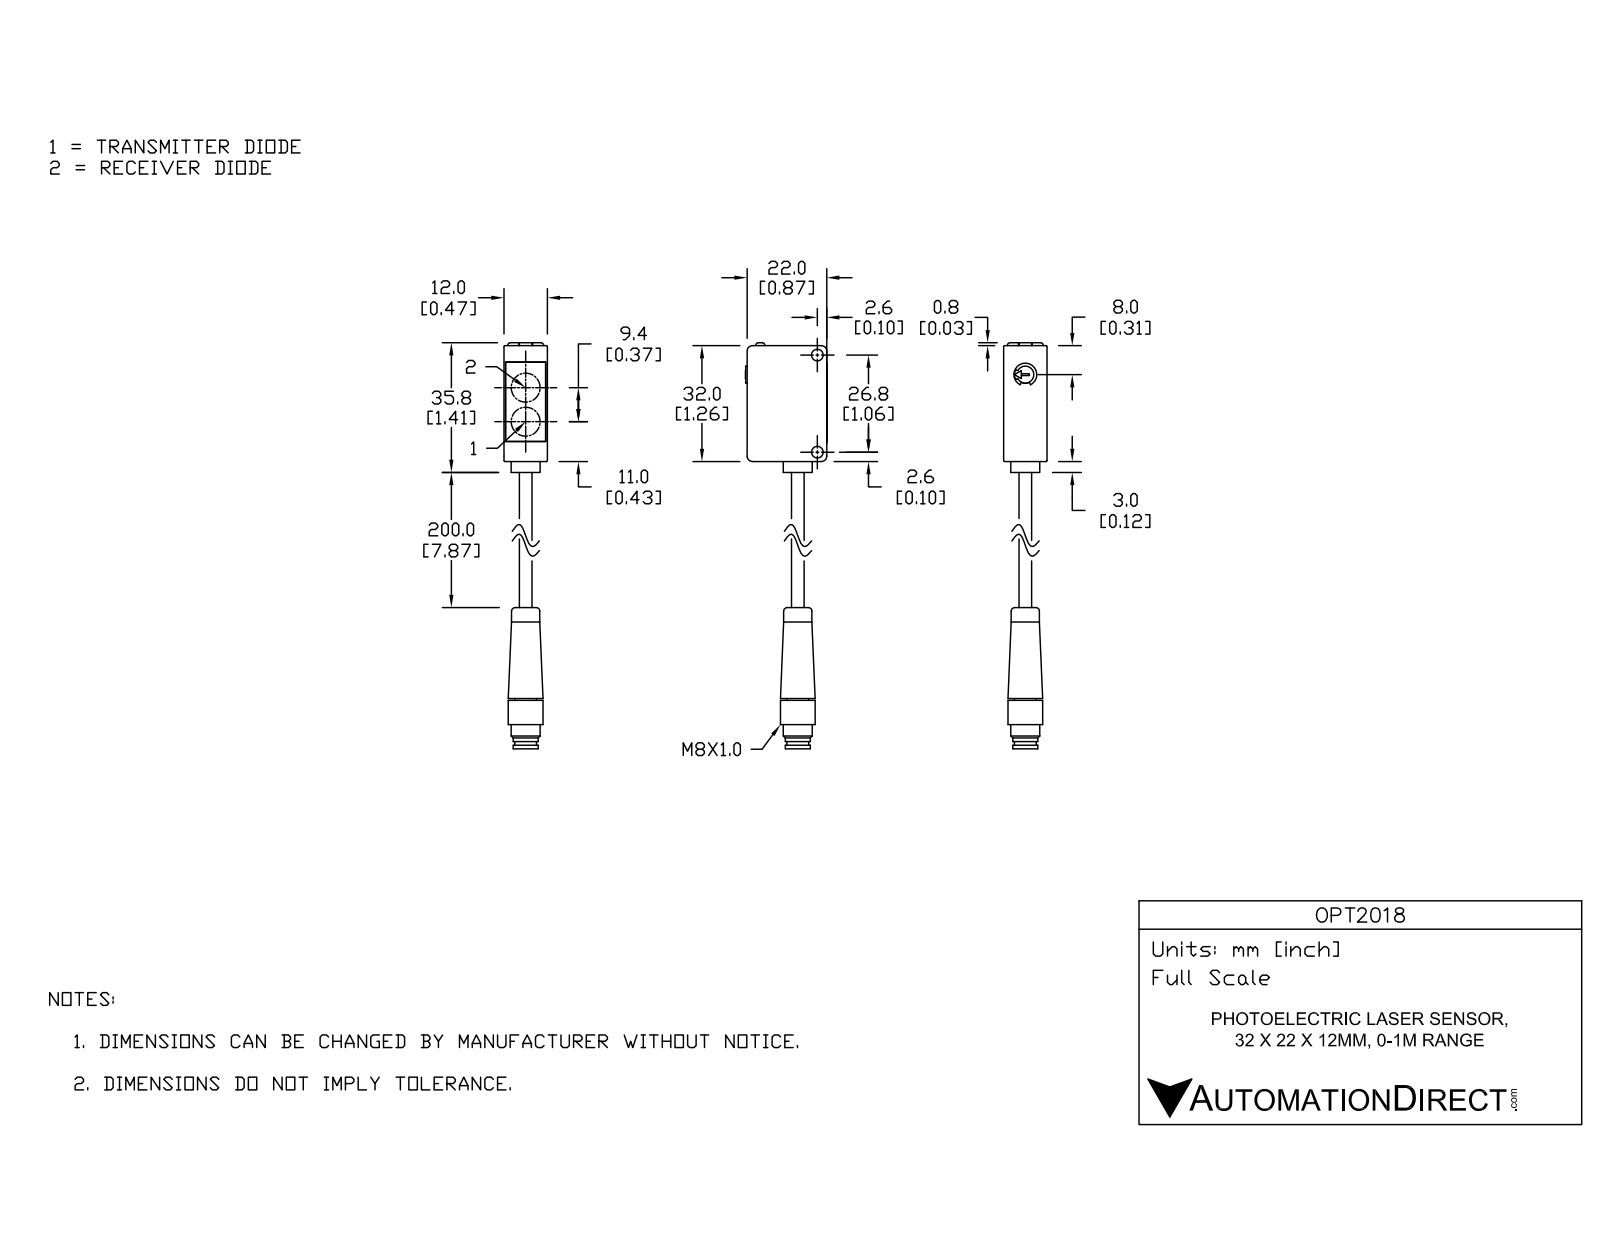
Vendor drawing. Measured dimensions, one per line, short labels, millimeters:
name: 1023033
written by: Unknown (AUTOMOTIVE_DESIGN)
unit: mm
bodies: 2 solids, 213 faces (101 planar, 78 cylindrical, 34 other)
size: 91.5 × 22.5 × 12
volume: 10 667 mm³; area: 4 789 mm²
holes: 2× ⌀3.2, 1× ⌀3.8, 1× ⌀5.8, 1× ⌀6.3
bosses: 4× ⌀1, 1× ⌀9.6, 1× ⌀8, 1× ⌀7.8, 1× ⌀6.9, 1× ⌀6, 1× ⌀4.7, 1× ⌀3.5
rounds: 8× R0.3, 4× R0.5, 4× R1.5, 2× R0.1, 2× R0.7, 2× R1.25, 1× R2.4, 1× R2.6
face distances: 12, 22.1, 32, 0.5, 22, 0.4, 11.5, 11.6, 11.1, 3
hole spacings: 26.8
